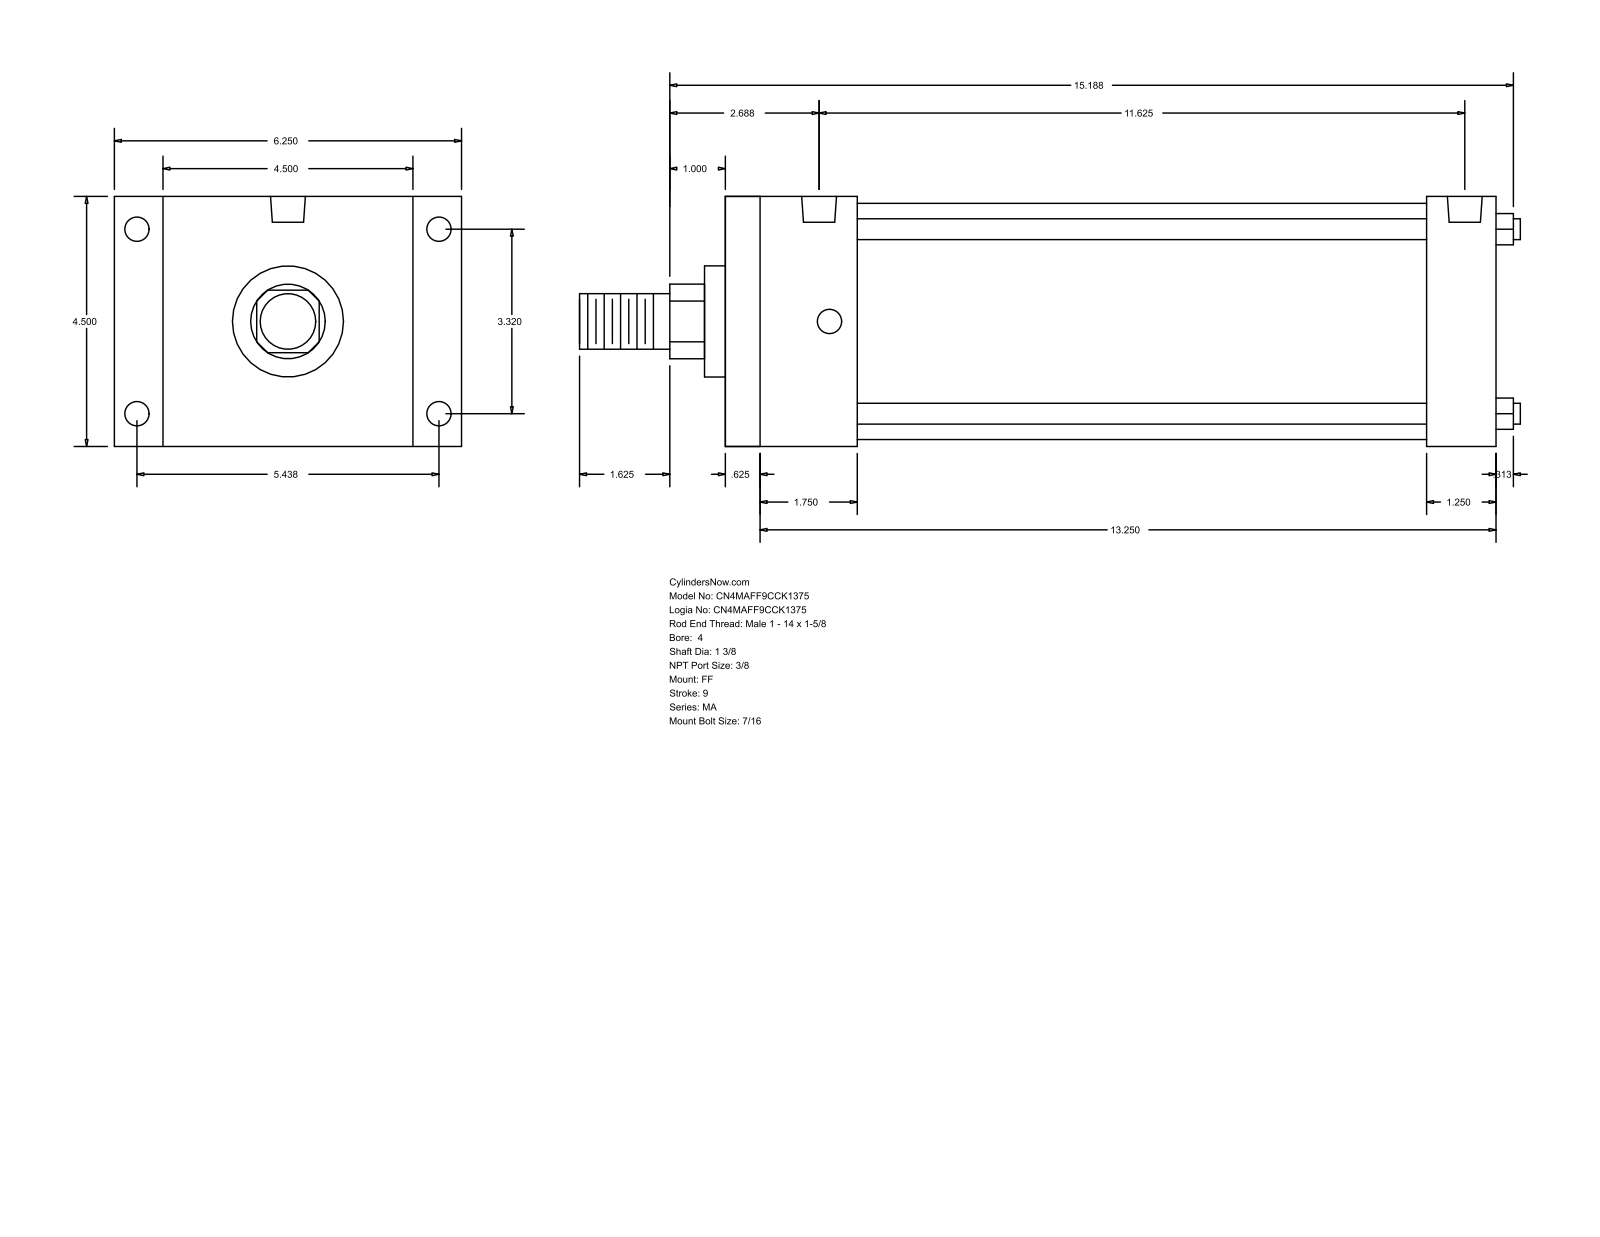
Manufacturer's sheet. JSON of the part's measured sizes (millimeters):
{"part_name": "MA_FF__0400_1.375", "step_written_by": "GSSL Pune (CONFIG_CONTROL_DESIGN)", "units": "millimeters", "bodies": {"solids": 0, "faces": 92, "planar": 64, "cylindrical": 28, "other": 0}, "overall_size": [430.21, 158.75, 114.3], "round_holes": [[11.11, 8], [15.93, 2]], "round_bosses_or_shafts": [[9.53, 4], [107.95, 1], [50.8, 1], [34.92, 1], [25.4, 1]], "partial_cylinders_radius": [[17.06, 1]], "face_to_face_distances": [114.3, 352.42, 15.87, 336.55, 22.23, 136.53, 320.67, 304.8, 31.75, 60.32], "hole_center_spacings": [4.77, 84.32, 138.12, 161.82, 285.74, 290.51, 295.28]}
